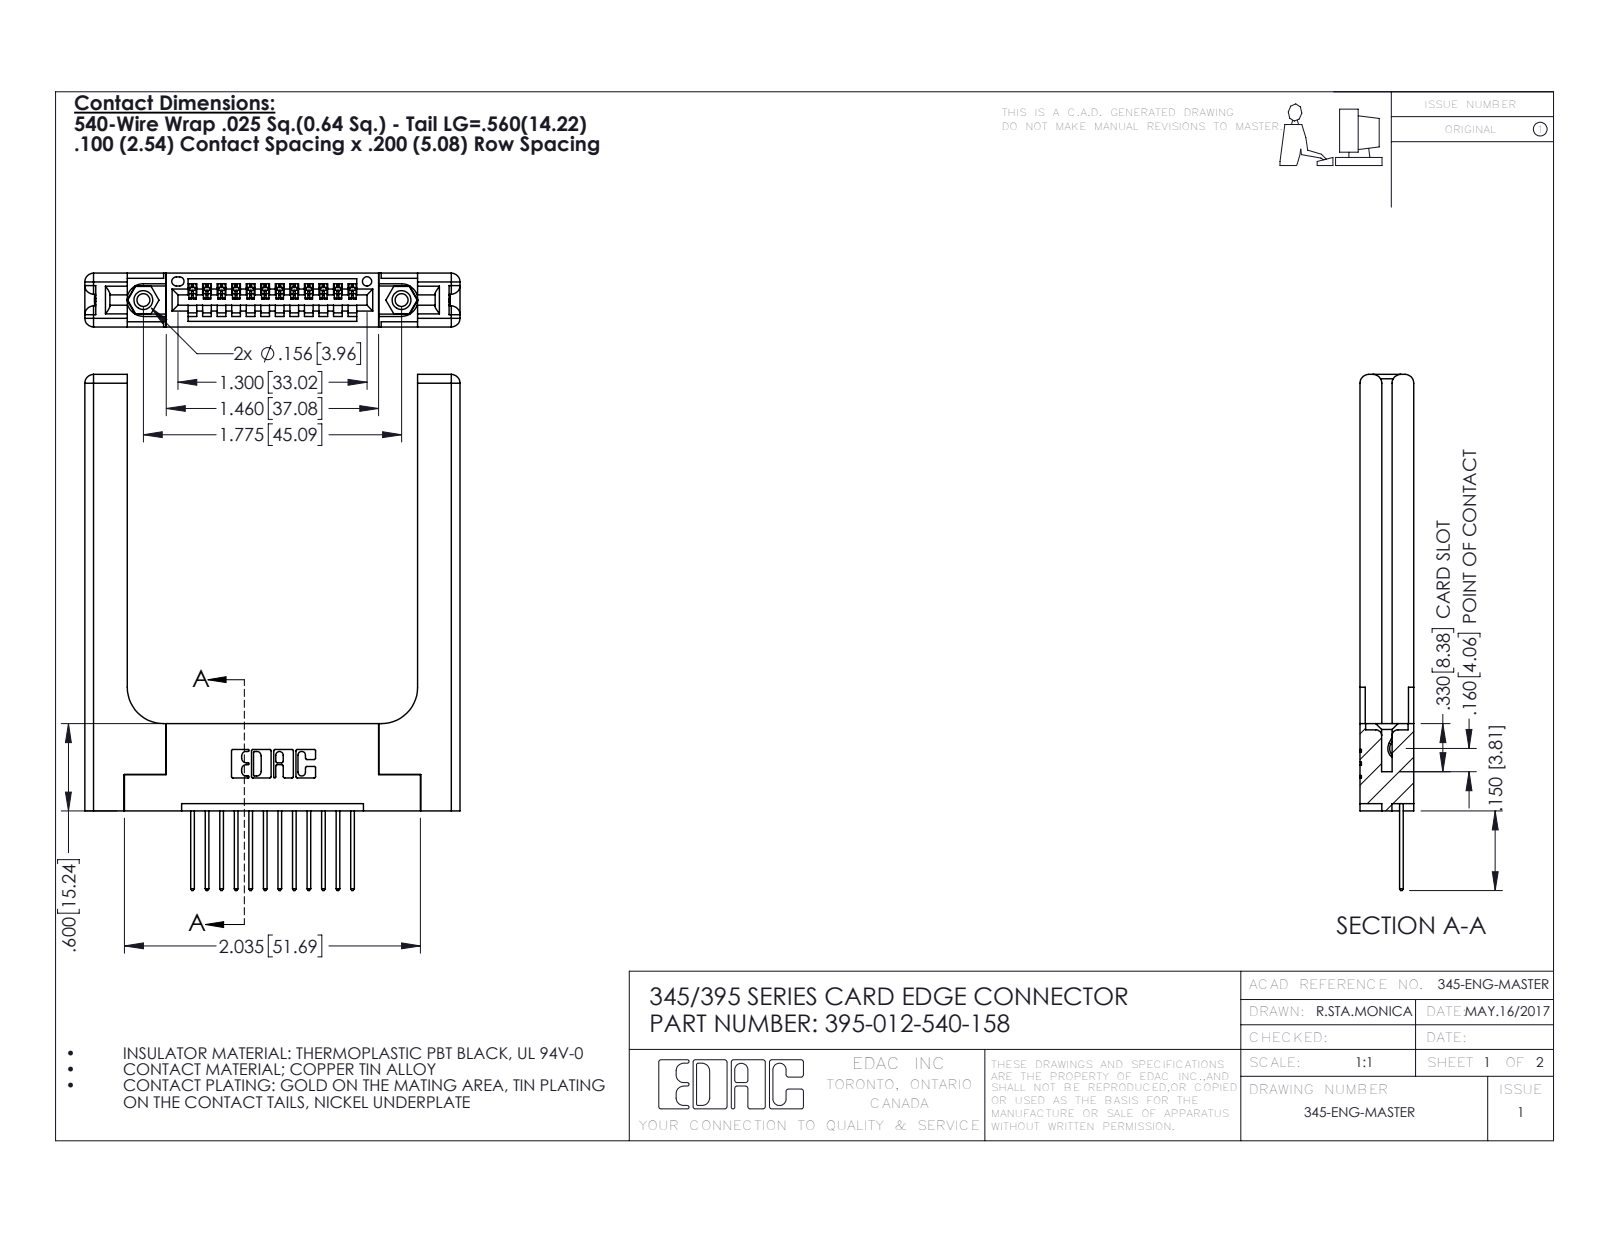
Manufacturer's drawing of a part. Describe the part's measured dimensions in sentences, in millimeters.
The part is named "345-292-001_345-293-140; 345-250-001_345-250-001-102; 395-012-540-158; 345 Part_Flush Mounting Lugs - 0.156 Dia-TH (+1 more)". Its 3-D file was written by "SolidWorks 2016 (CONFIG_CONTROL_DESIGN)". It is 17 solids with 1078 faces: 708 planar, 310 cylindrical and 60 other. Overall it measures 90.1 by 65.5 by 9.4 millimeters. Its volume is 14 500 cubic millimeters and its surface area 12 980 square millimeters. Round holes: 2 of diameter 2.3, 2 of diameter 3.2, 2 of diameter 4, 1 of diameter 1.6. Round bosses or shafts: 2 of diameter 3.9. Partial cylindrical surfaces (rounded edges, fillets, slot ends): 24 of radius 0.2, 24 of radius 0.3, 22 of radius 0.3, 16 of radius 1.5, 6 of radius 0.2, 6 of radius 0.8, 3 of radius 0.7, 2 of radius 0.8. The main face-to-face distances are 9.4, 1.8, 3.8, 7.6, 5.6, 2, 3.8, 5.1, 50.7, 2.5. The hole center spacings are 6.9, 39.2, 45.1.
